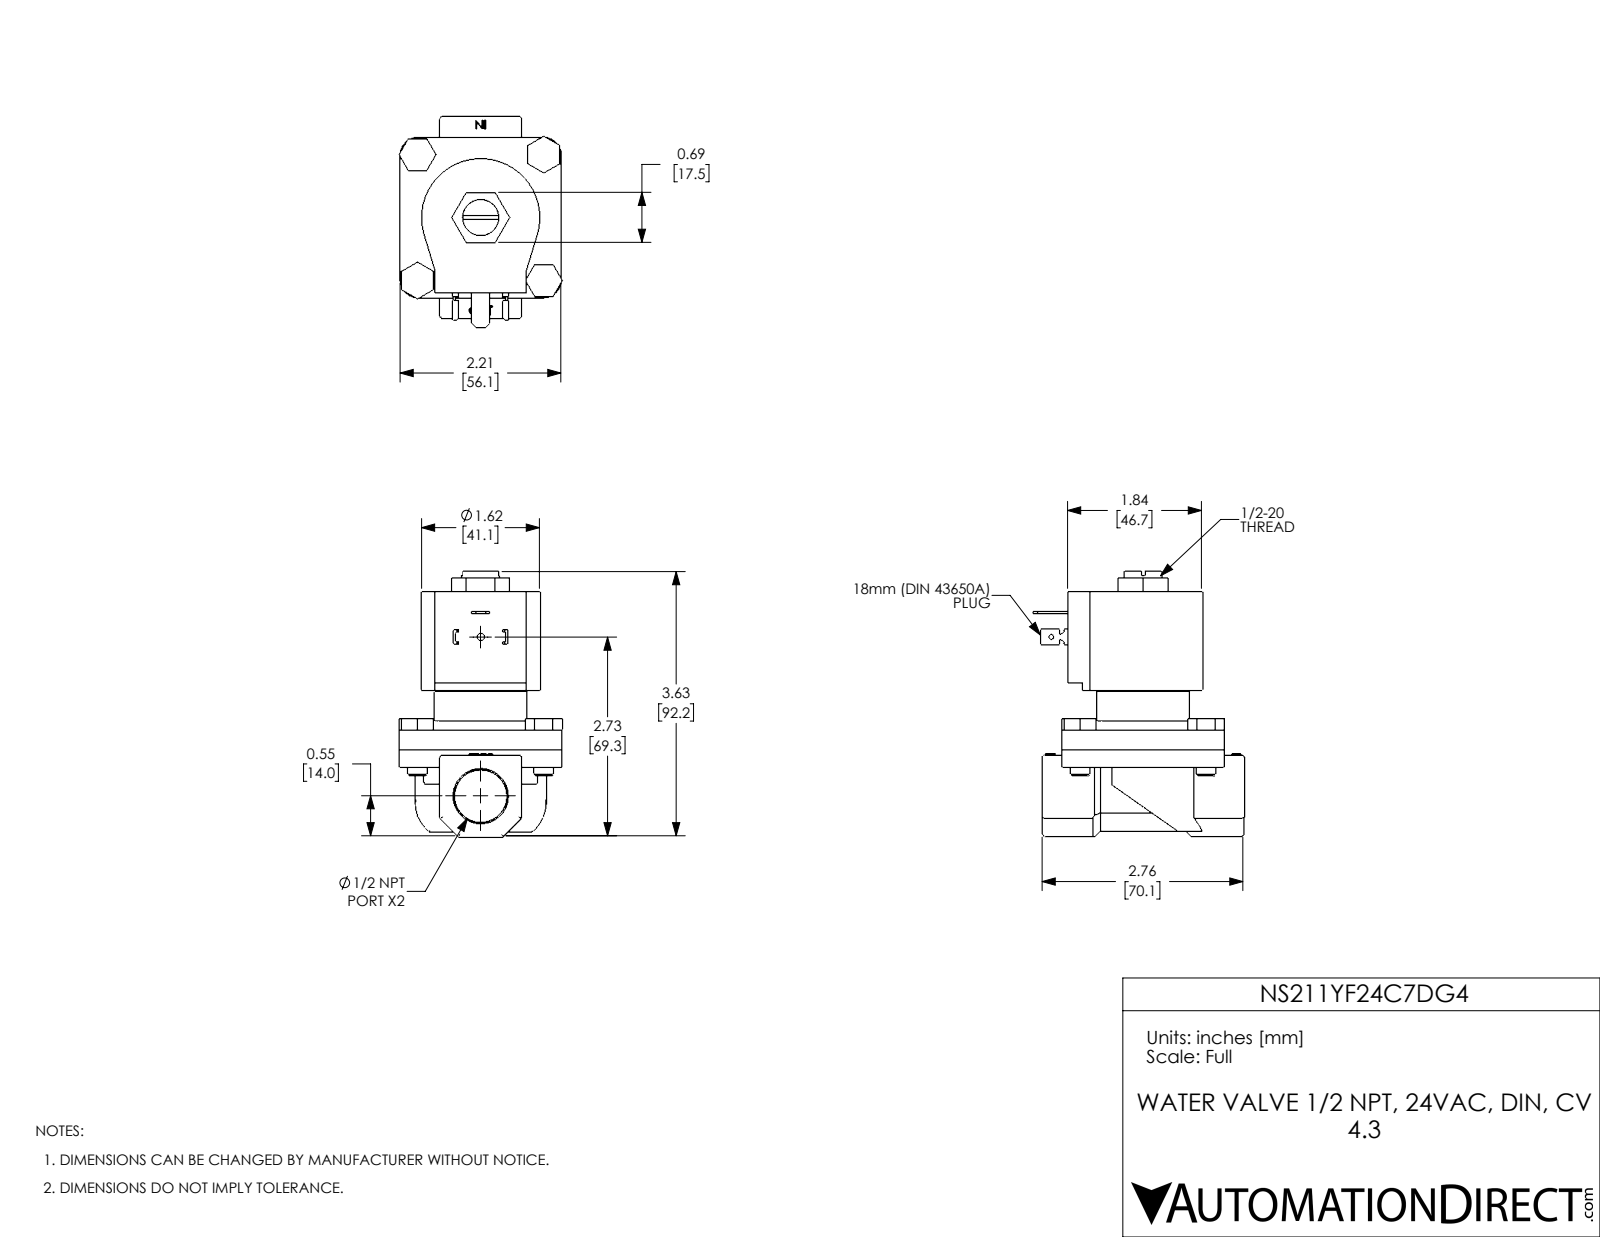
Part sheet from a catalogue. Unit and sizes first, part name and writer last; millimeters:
Units: millimetres
Overall size (bounding box): 92.2 × 73.4 × 56.8
Round holes (diameter × count): ⌀6.4 ×4, ⌀1.7 ×1, ⌀2.5 ×1, ⌀12.6 ×1, ⌀13 ×1, ⌀18.3 ×1, ⌀29.3 ×1
Round bosses / shafts (diameter × count): ⌀6.3 ×4, ⌀31.8 ×1
Partial cylindrical surfaces — rounded edges, fillets, slot ends (radius × count): R0.8 ×15, R0.4 ×8, R6.4 ×4, R1.5 ×2, R20.6 ×1, R22.6 ×1
Main face-to-face distances: 7, 55.1, 48.1, 14.1, 42.1, 6, 13, 61.1, 56.1, 28
Hole centre spacings: 31.1, 43.9, 62.1, 55.4
Volume: 150 700 mm³ · Surface area: 39 340 mm²
Bodies: 11 solids, 330 faces (196 planar, 99 cylindrical, 35 other)
Part name (STEP PRODUCT): NS211YF24C7DG4
STEP written by: SolidWorks 2021 (CONFIG_CONTROL_DESIGN)
